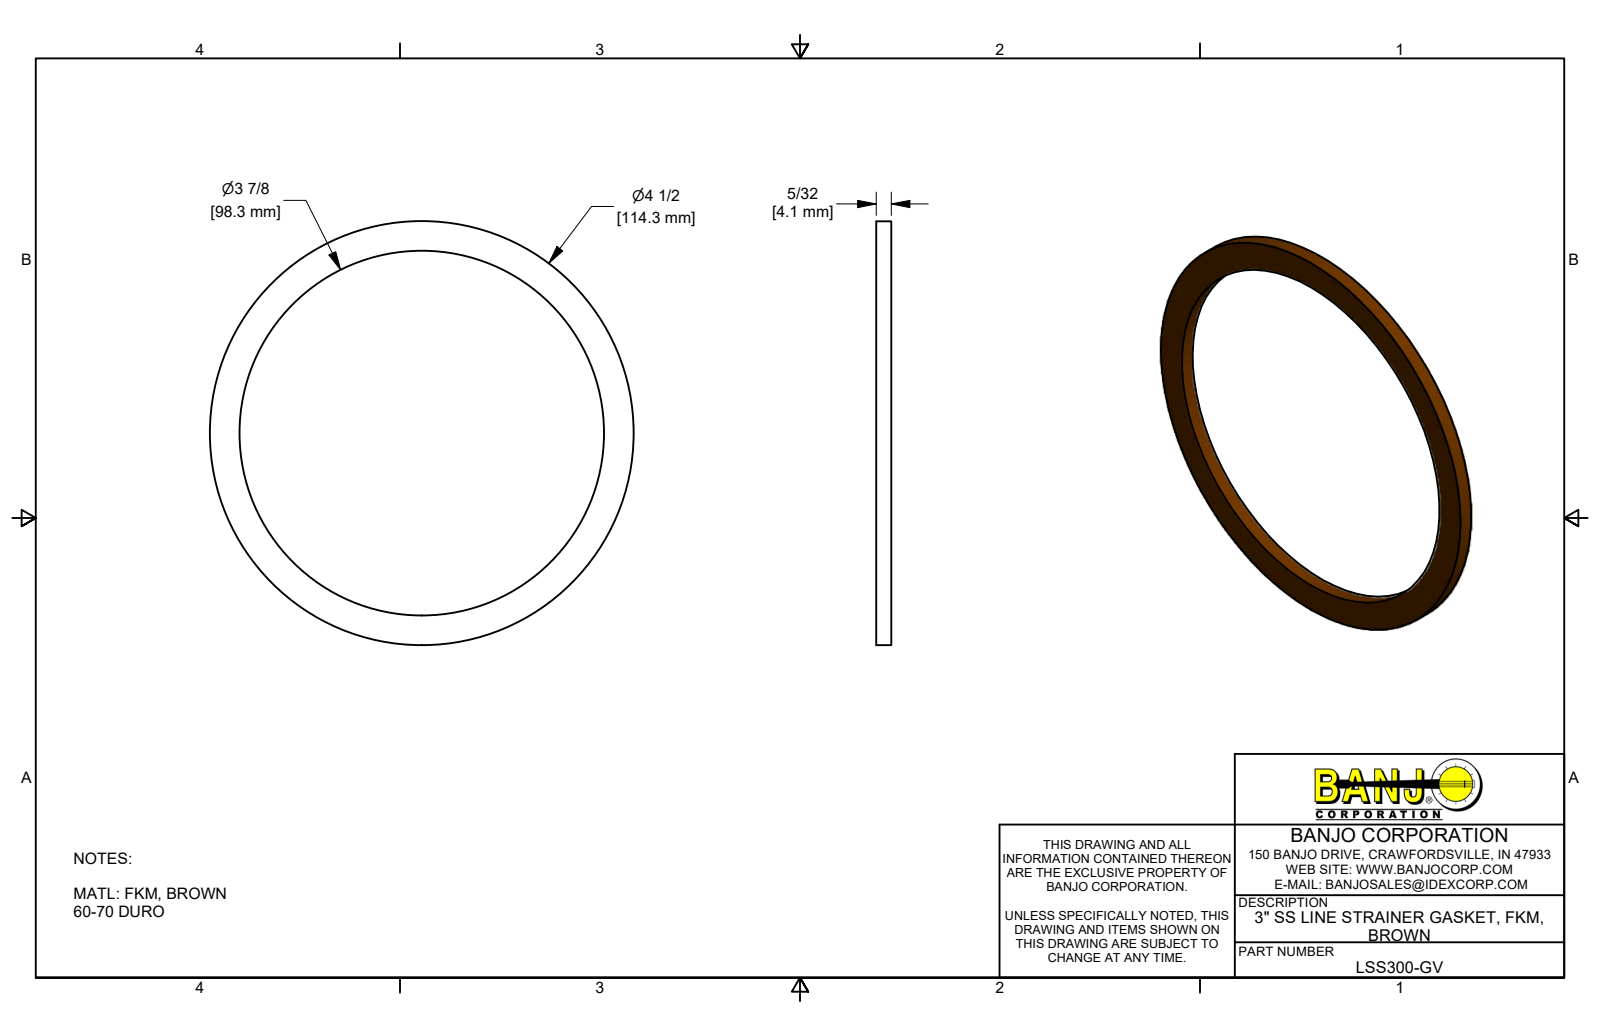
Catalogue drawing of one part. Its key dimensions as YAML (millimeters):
part_name: "LSS300-GV"
step_written_by: "Autodesk Inventor 2019 (AUTOMOTIVE_DESIGN)"
units: millimeters
bodies: {solids: 1, faces: 4, planar: 2, cylindrical: 2, other: 0}
overall_size: [114.3, 114.3, 4.1]
volume: 10900
surface_area: 8058
round_holes:
  - {diameter: 98.3, count: 1}
round_bosses_or_shafts:
  - {diameter: 114.3, count: 1}
face_to_face_distances: [4.1]
